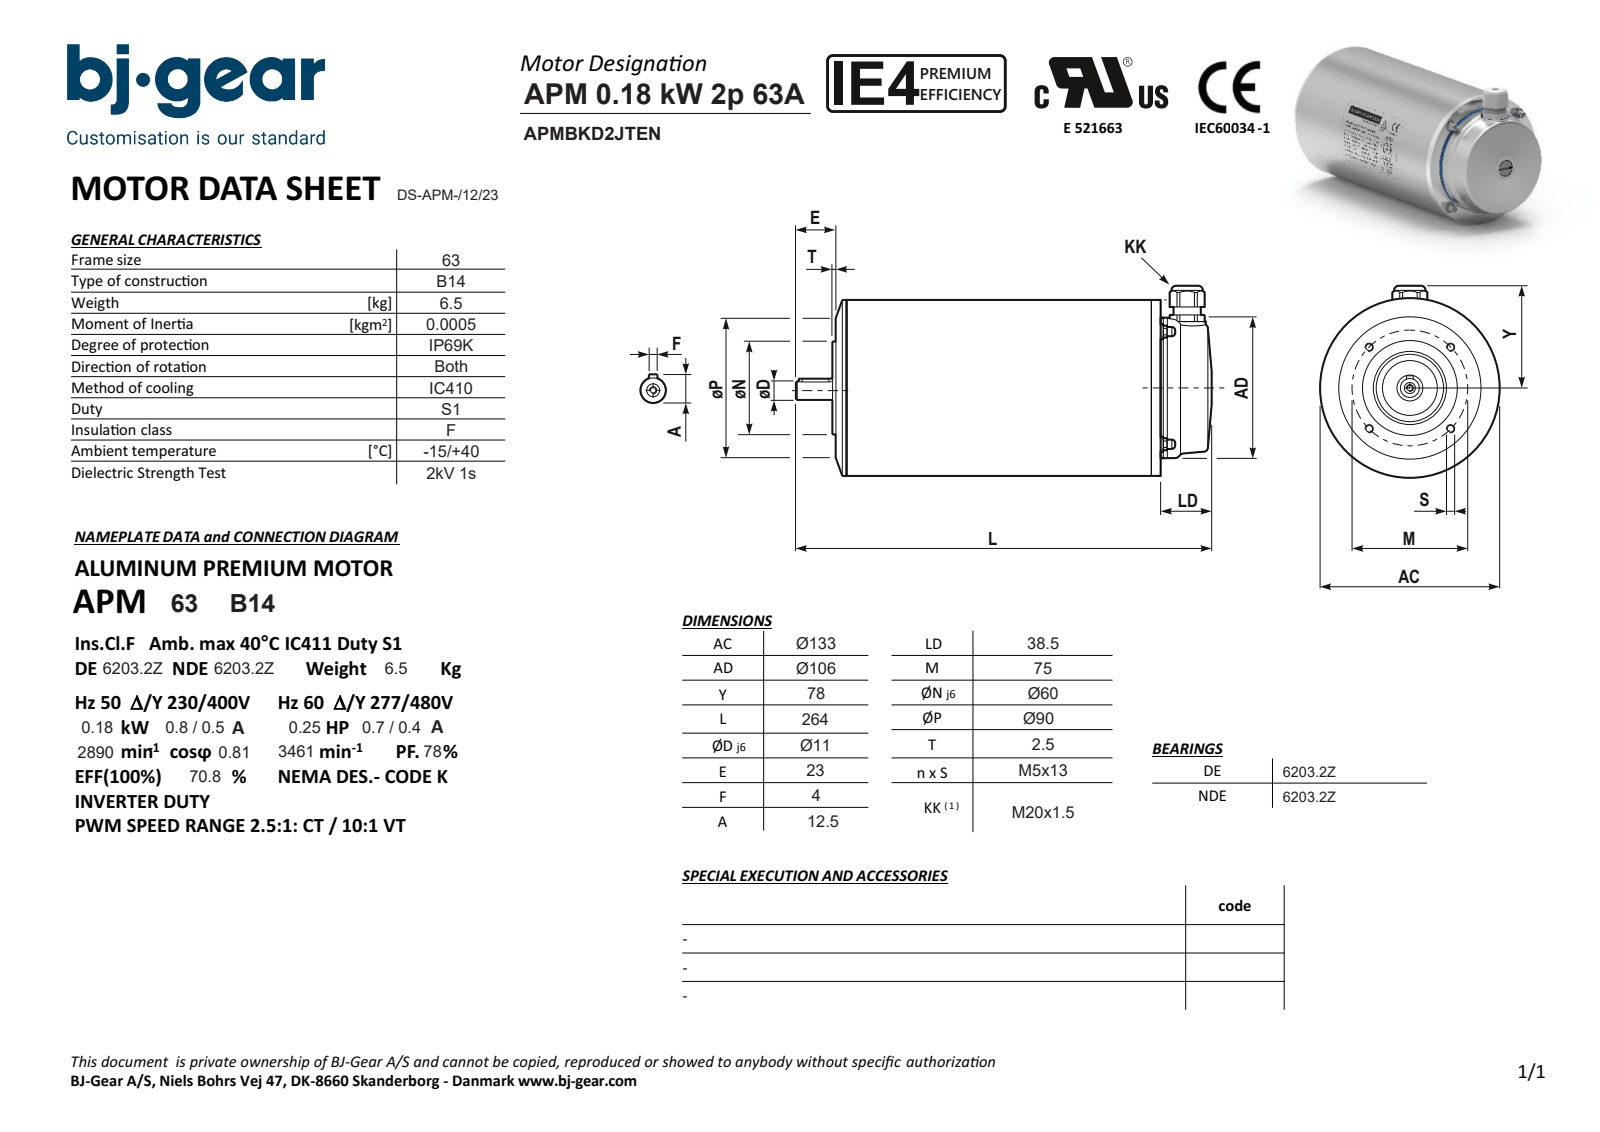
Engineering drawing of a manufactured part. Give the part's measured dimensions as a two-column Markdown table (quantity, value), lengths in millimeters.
| quantity | value |
| --- | --- |
| part name | APMBKD2JTENN4KCR2-N---NNN |
| STEP written by | Solid Edge (AUTOMOTIVE_DESIGN) |
| units | millimeters |
| bodies | 1 solid, 156 faces (71 planar, 50 cylindrical, 35 other) |
| overall size | 264 × 143.3 × 132.6 |
| volume | 3 075 000 mm³ |
| surface area | 127 331 mm² |
| round holes (diameter × count) | 4.13 × 4, 3.24 × 1, 4.3 × 1, 16 × 1, 28 × 1, 52 × 1 |
| round bosses / shafts (diameter × count) | 11.5 × 4, 7 × 4, 132.6 × 1, 132.6 × 1, 106 × 1, 60 × 1, 23.7 × 1, 20.6 × 1 |
| partial cylindrical surfaces (radius × count) | 2 × 2, 13.2 × 1 |
| main face-to-face distances | 202.5, 197, 5.5, 8, 2.5, 205, 38.5, 235.5, 241, 243.5 |
| hole center spacings | 37.5, 53.04, 75.01 |
